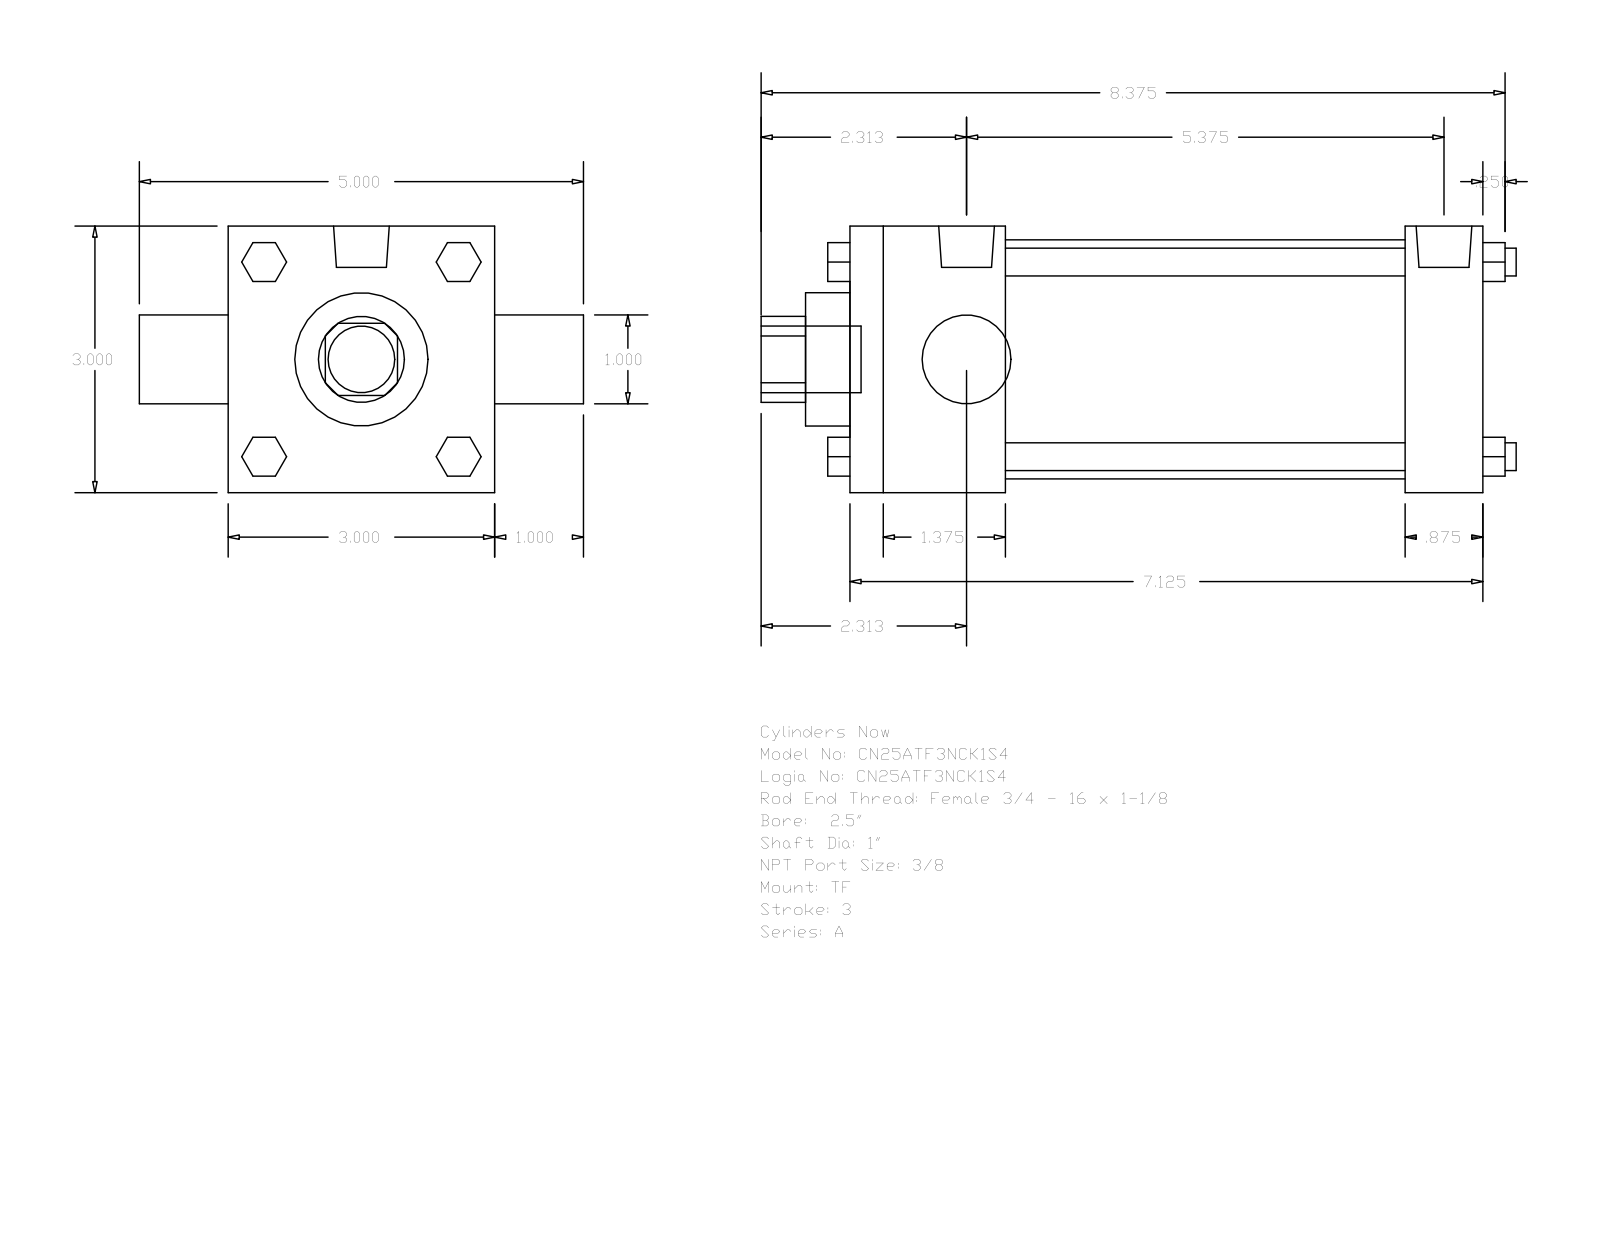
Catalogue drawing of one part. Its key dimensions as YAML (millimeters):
part_name: "A_TF__0250_1"
step_written_by: "GSSL Pune (CONFIG_CONTROL_DESIGN)"
units: millimeters
bodies: {solids: 0, faces: 120, planar: 92, cylindrical: 28, other: 0}
overall_size: [215.9, 127, 76.2]
round_holes:
  - {diameter: 25.4, count: 2}
  - {diameter: 38.1, count: 1}
  - {diameter: 68.33, count: 1}
round_bosses_or_shafts:
  - {diameter: 7.94, count: 4}
  - {diameter: 5.56, count: 3}
  - {diameter: 15.93, count: 2}
  - {diameter: 19.05, count: 1}
partial_cylinders:
  - {radius: 12.29, count: 1}
face_to_face_distances: [76.2, 180.98, 44.45, 158.75, 114.3, 136.53, 22.23, 25.4, 101.6, 12.7]
